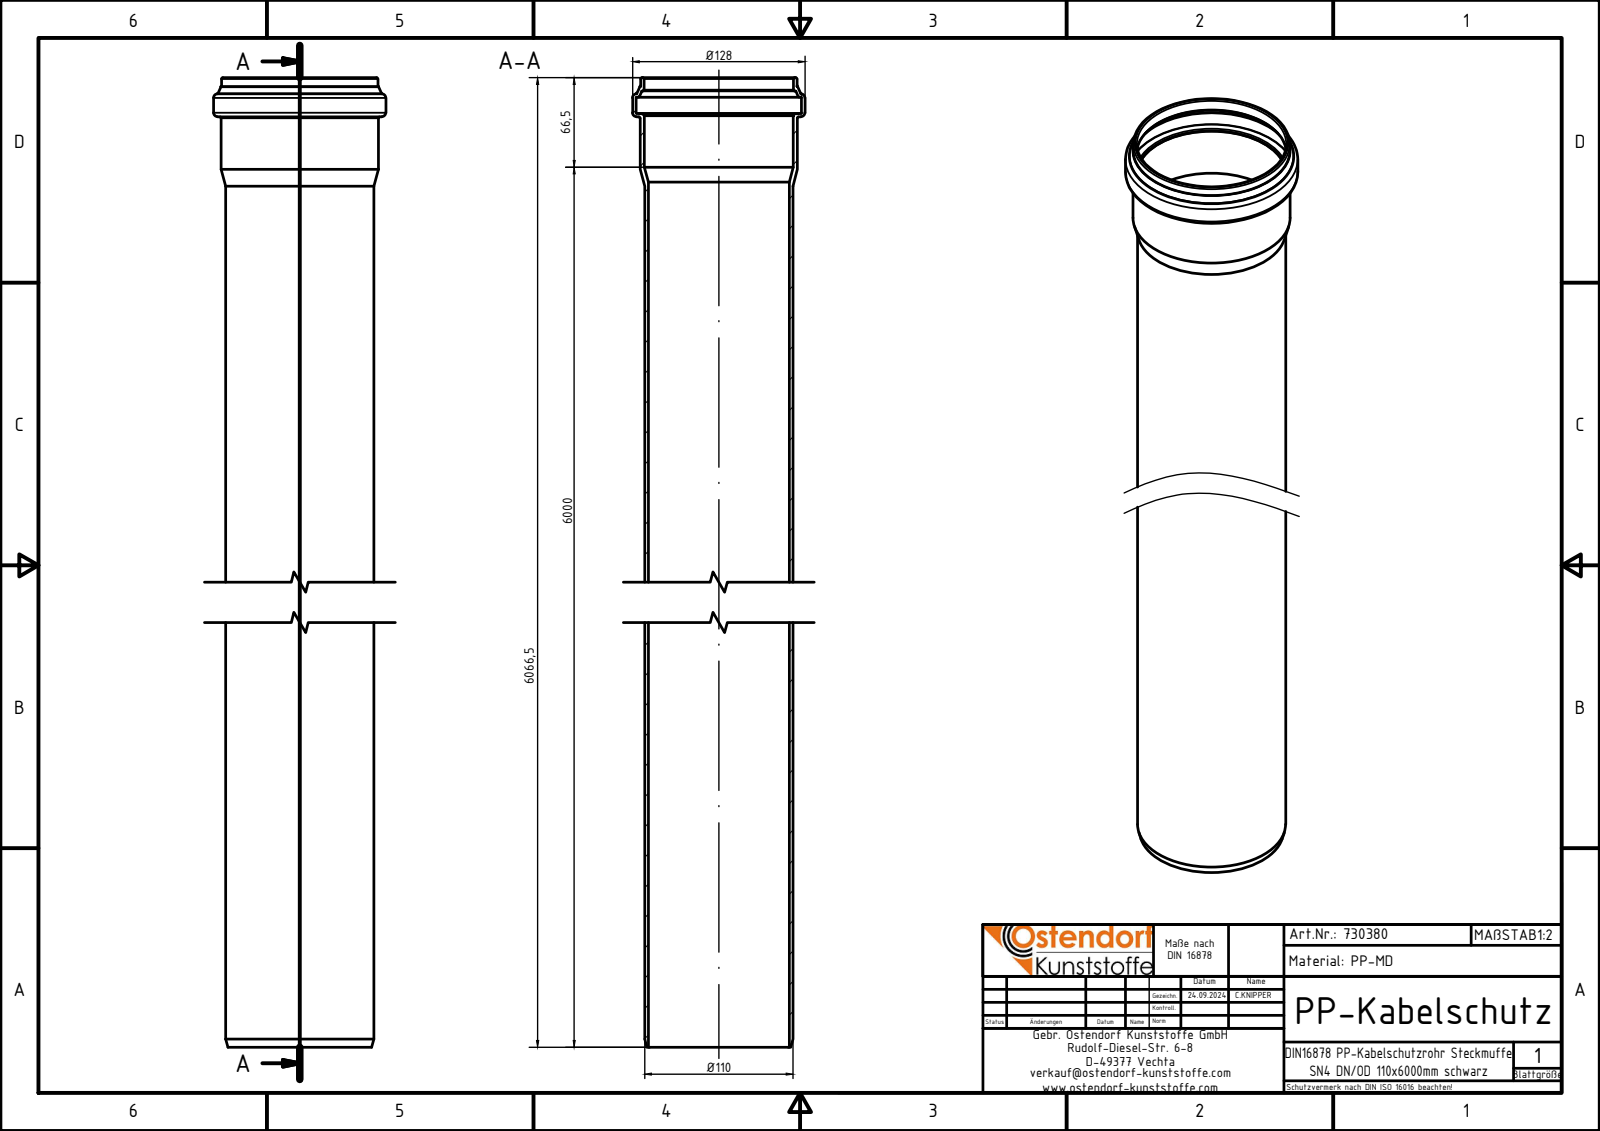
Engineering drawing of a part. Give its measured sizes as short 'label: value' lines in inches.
name: 730380z
written by: Autodesk Inventor 2024 (AUTOMOTIVE_DESIGN)
unit: in
bodies: 1 solid, 36 faces (5 planar, 9 cylindrical, 22 other)
size: 238.839 × 5.039 × 5.039
volume: 338.1 in³; area: 6 357 in²
holes: 1× ⌀4.118, 1× ⌀4.35, 1× ⌀4.366, 1× ⌀4.835
bosses: 1× ⌀5.039, 1× ⌀4.594, 1× ⌀4.571, 1× ⌀4.331
face distances: 237.693, 238.839, 1.146, 237.725, 0.032, 1.113, 238.577, 0.884, 0.852, 0.262
